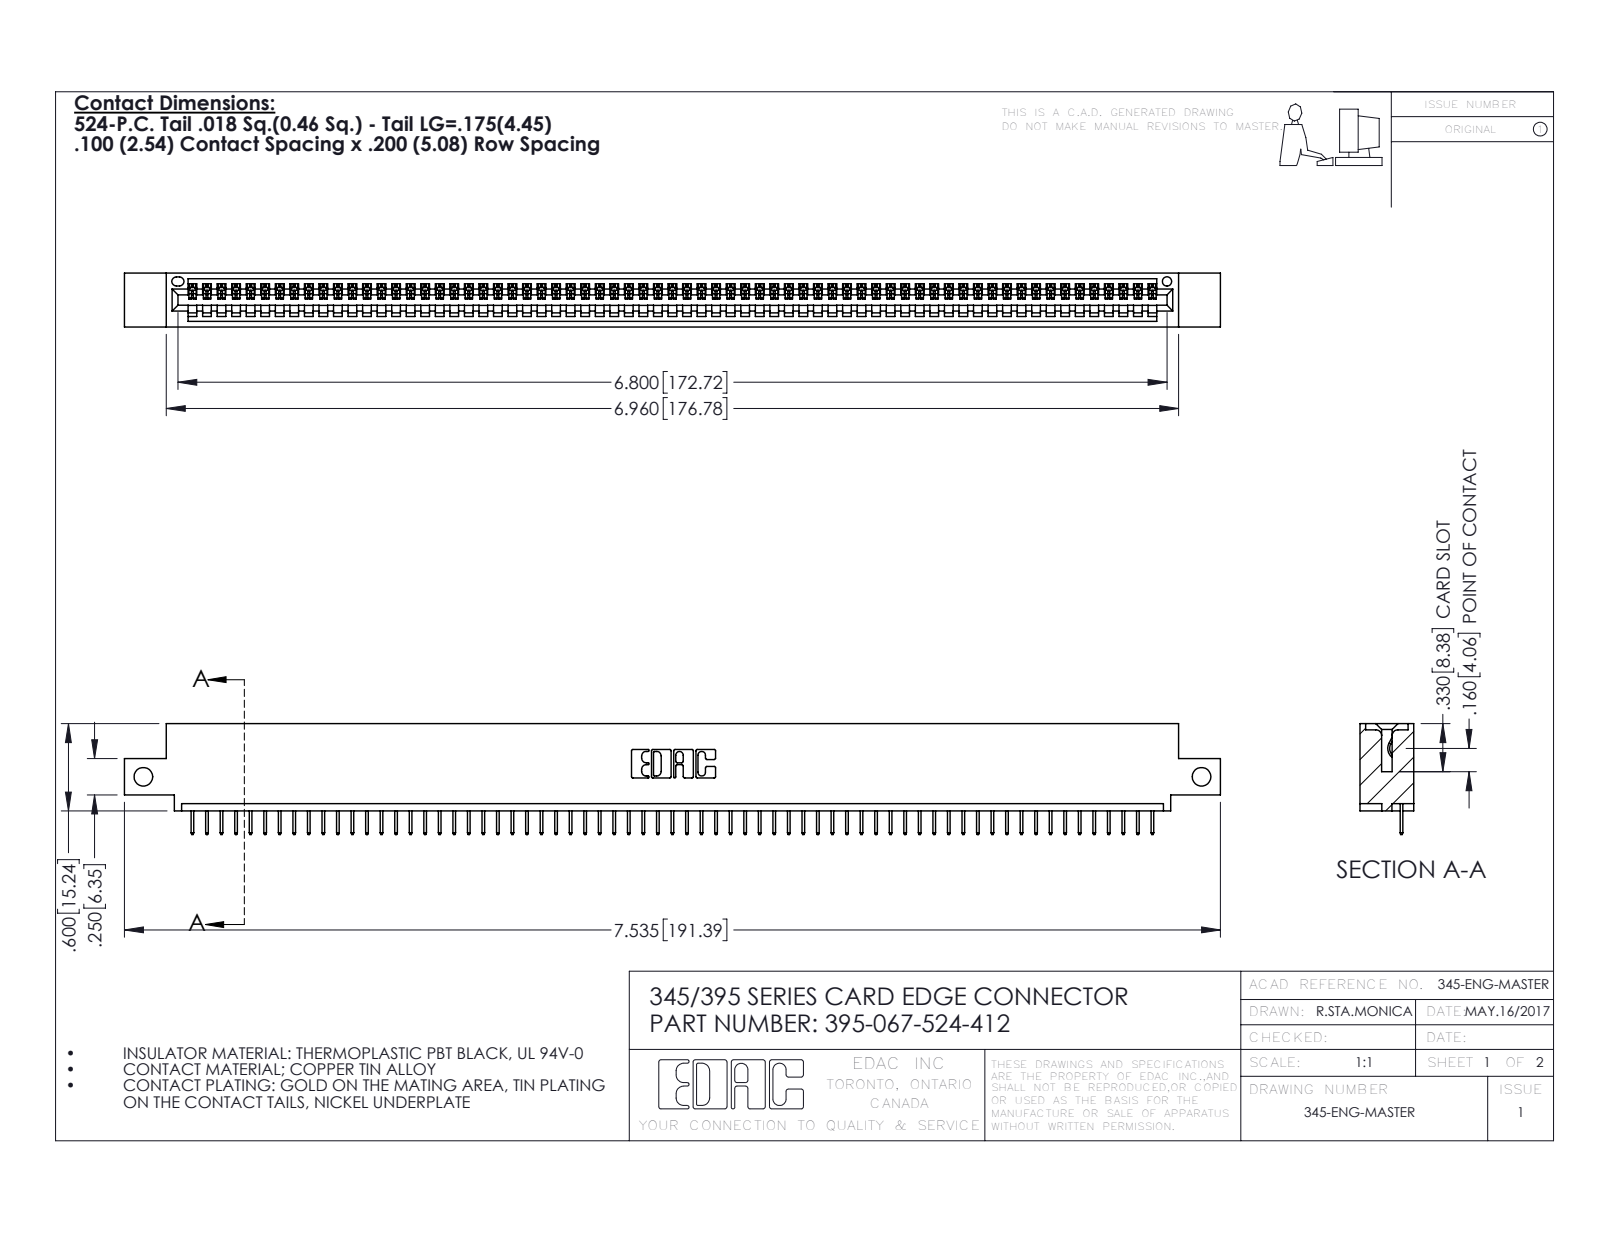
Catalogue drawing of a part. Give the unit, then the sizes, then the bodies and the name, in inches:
Units: inches
Overall size (bounding box): 7.535 × 0.762 × 0.37
Round holes (diameter × count): ⌀0.128 ×2, ⌀0.064 ×1
Partial cylindrical surfaces — rounded edges, fillets, slot ends (radius × count): R0.006 ×134, R0.01 ×22, R0.007 ×6, R0.031 ×6, R0.026 ×3, R0.031 ×2, R0.04 ×2, R0.014 ×1
Main face-to-face distances: 0.072, 0.298, 0.37, 0.2, 0.098, 0.272, 0.025, 0.225, 0.072, 0.149
Hole centre spacings: 7.275
Volume: 1.096 in³ · Surface area: 36.11 in²
Bodies: 68 solids, 4284 faces (3166 planar, 1118 cylindrical, 0 other)
Part name (STEP PRODUCT): 345 Part_0.110 Offset - Side Mount; 395-067-524-412; 345-292-001_345-293-124
STEP written by: SolidWorks 2016 (CONFIG_CONTROL_DESIGN)
